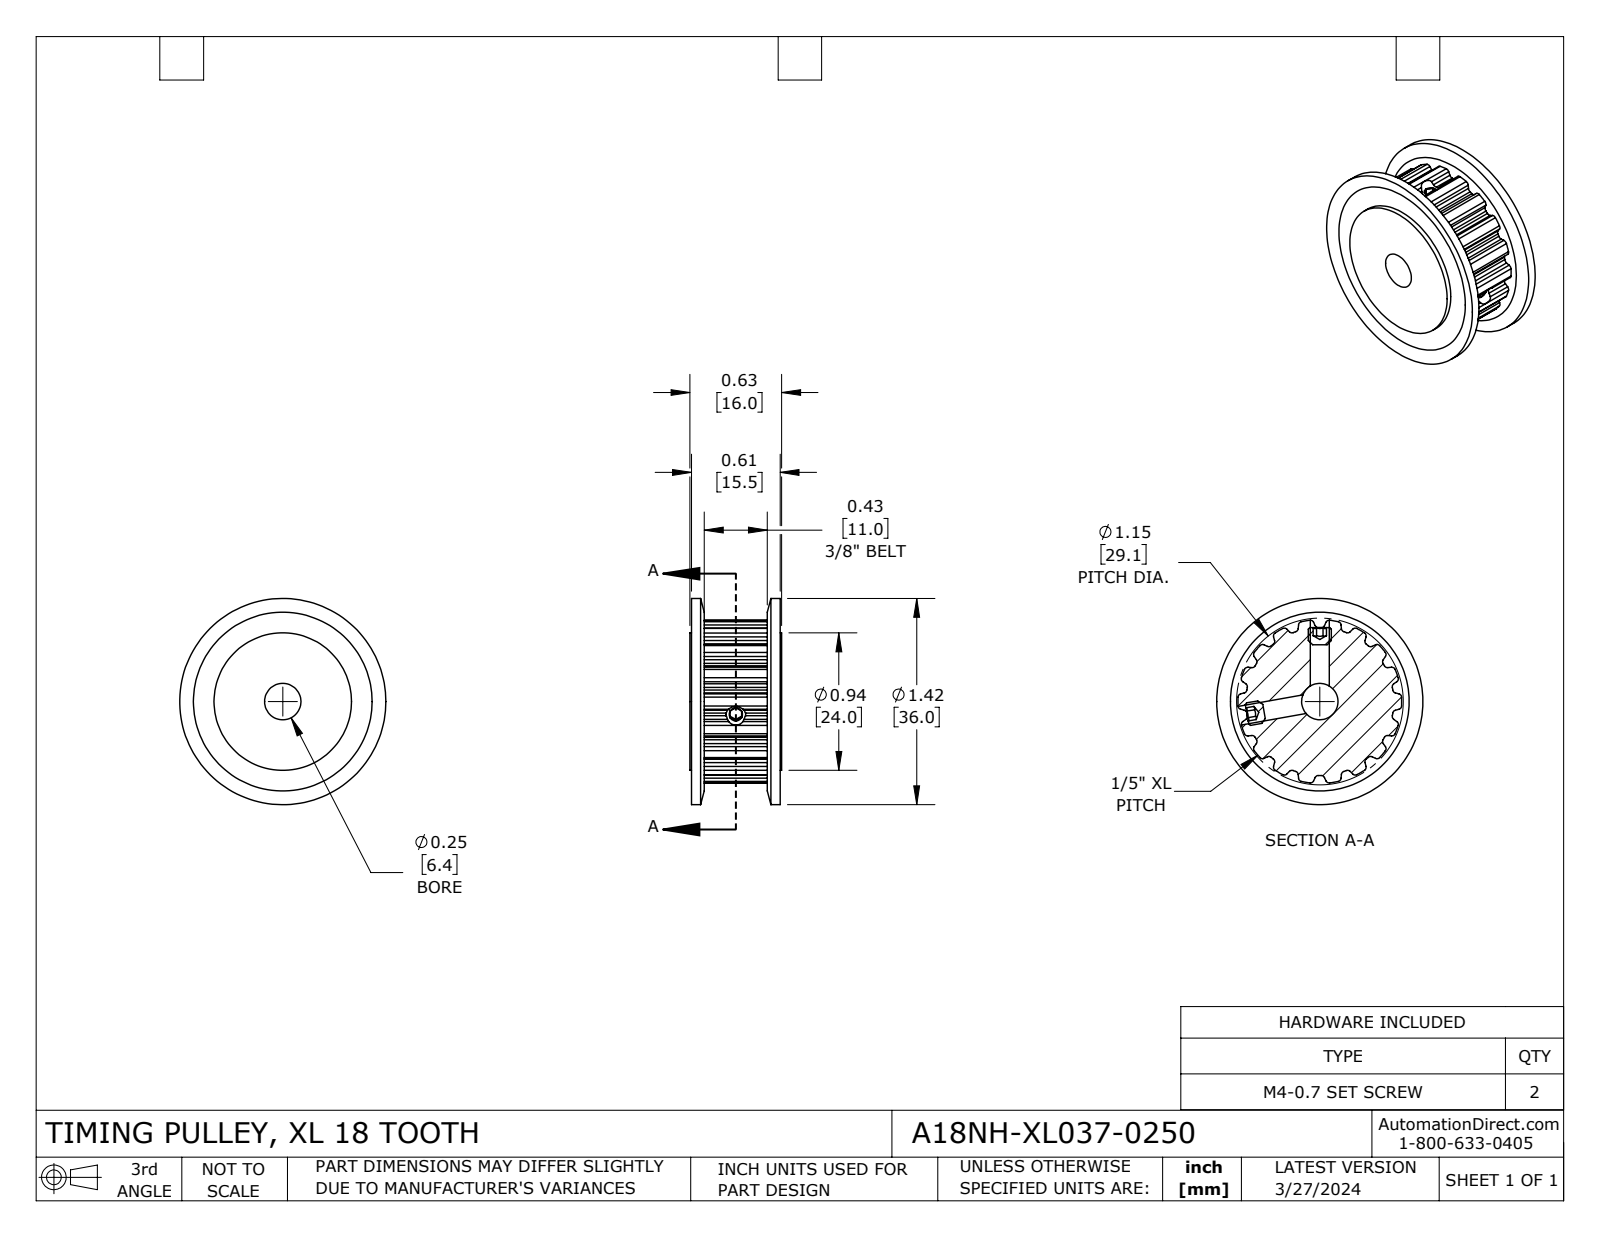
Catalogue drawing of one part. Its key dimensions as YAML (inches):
part_name: "A18NH-XL037-0250"
step_written_by: "SolidWorks 2021 (CONFIG_CONTROL_DESIGN)"
units: inches
bodies: {solids: 5, faces: 248, planar: 64, cylindrical: 150, other: 34}
overall_size: [1.417, 1.417, 0.63]
volume: 0.609
surface_area: 9.736
round_holes:
  - {diameter: 0.13, count: 2}
  - {diameter: 0.25, count: 1}
  - {diameter: 0.945, count: 1}
round_bosses_or_shafts:
  - {diameter: 0.157, count: 2}
  - {diameter: 1.417, count: 1}
partial_cylinders:
  - {radius: 0.024, count: 72}
  - {radius: 0.508, count: 1}
  - {radius: 0.563, count: 1}
face_to_face_distances: [0.098, 0.531, 0.035, 0.594, 0.063, 0.496, 0.433, 0.63, 0.559, 0.383]
